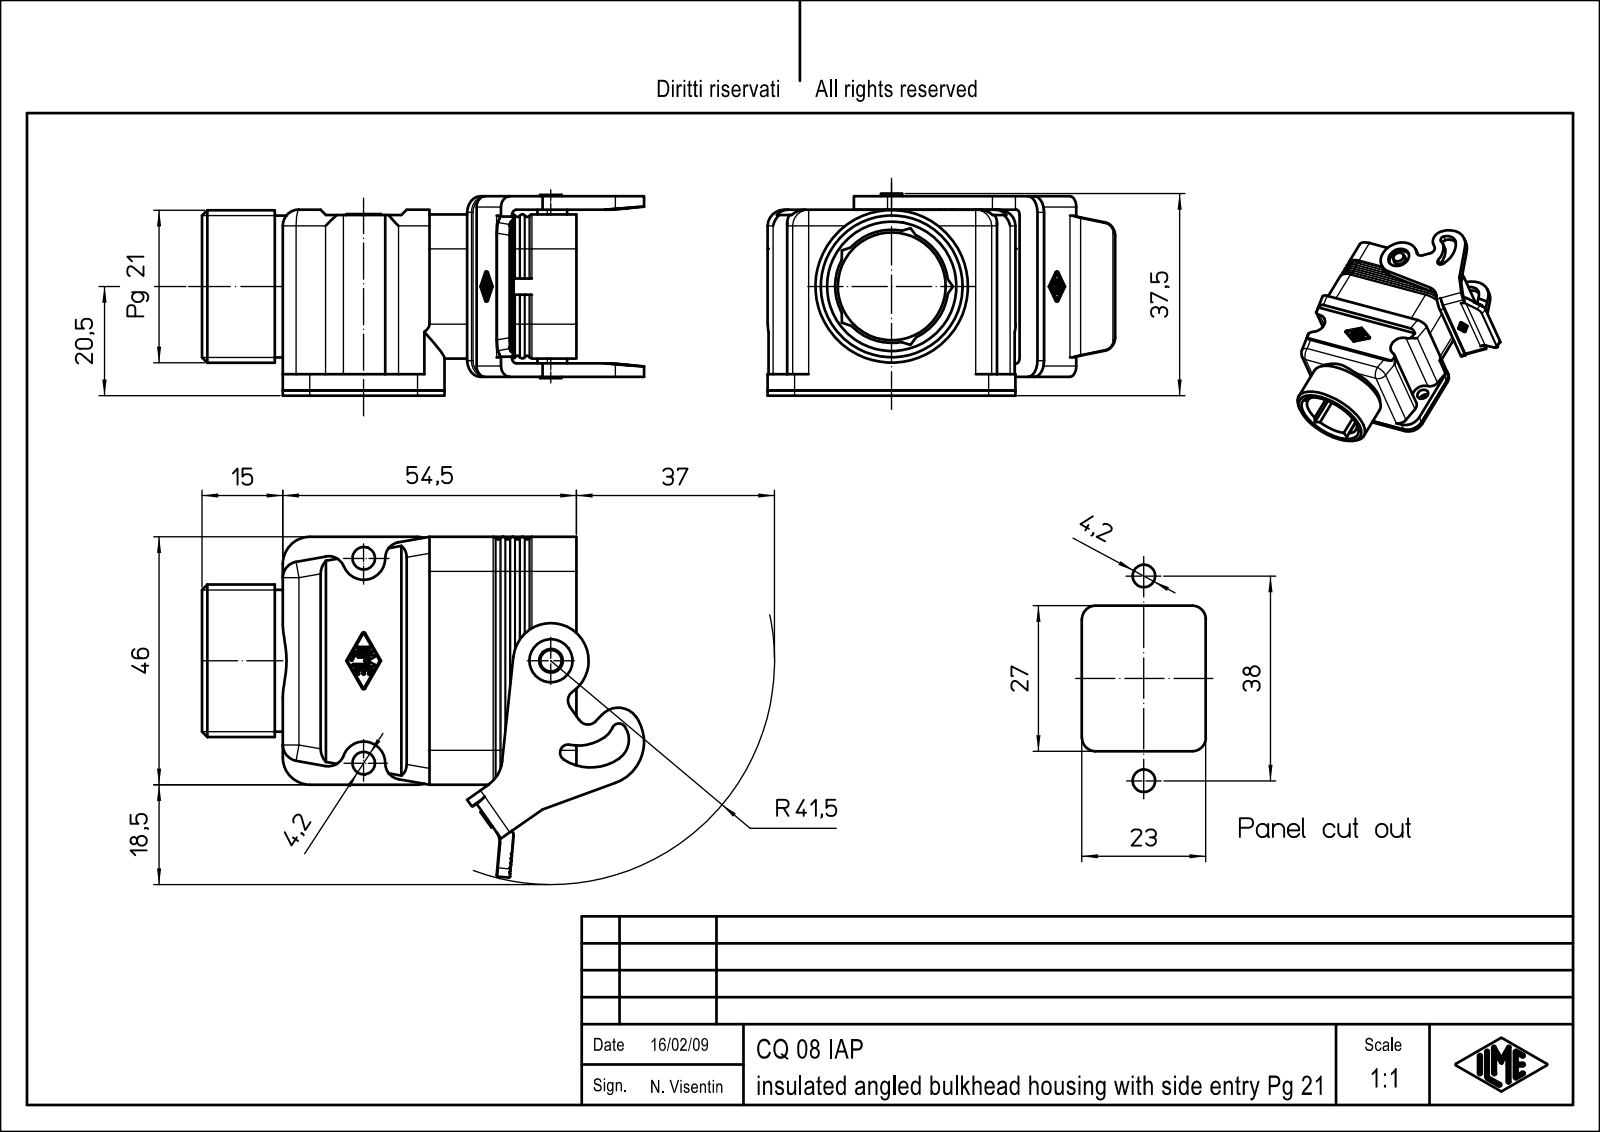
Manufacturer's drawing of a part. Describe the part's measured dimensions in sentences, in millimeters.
The part is named "CUSTODIA_CQ_08_IAP; LEVA_CQ_08_IAP; CQ_08_IAP". Its 3-D file was written by "CoCreate Modeling 16.00A 16-Aug-2008 (C) Parametric Technology GmbH (AUTOMOTIVE_DESIGN)". It is 2 solids with 721 faces: 282 planar, 293 cylindrical and 146 other. Overall it measures 82.05 by 63.2 by 37.25 millimeters. Its volume is 30 860 cubic millimeters and its surface area 25 762 square millimeters. Round holes: 4 of diameter 2.4, 4 of diameter 2.5, 4 of diameter 3.1, 2 of diameter 4.2, 1 of diameter 4.4, 1 of diameter 8, 1 of diameter 20. Round bosses or shafts: 1 of diameter 28.3, 1 of diameter 26.31, 1 of diameter 4. Partial cylindrical surfaces (rounded edges, fillets, slot ends): 36 of radius 0.5, 14 of radius 0.1, 14 of radius 3, 13 of radius 0.2, 9 of radius 2, 5 of radius 2.5, 4 of radius 1.7, 4 of radius 4.5. The main face-to-face distances are 2.5, 27.5, 33.5, 2.75, 25.75, 2, 3.5, 5.25, 28.25, 31. The hole center spacings are 7.3, 13.4, 17.44, 32.2, 34.88, 35.73, 32.34, 39.61.
